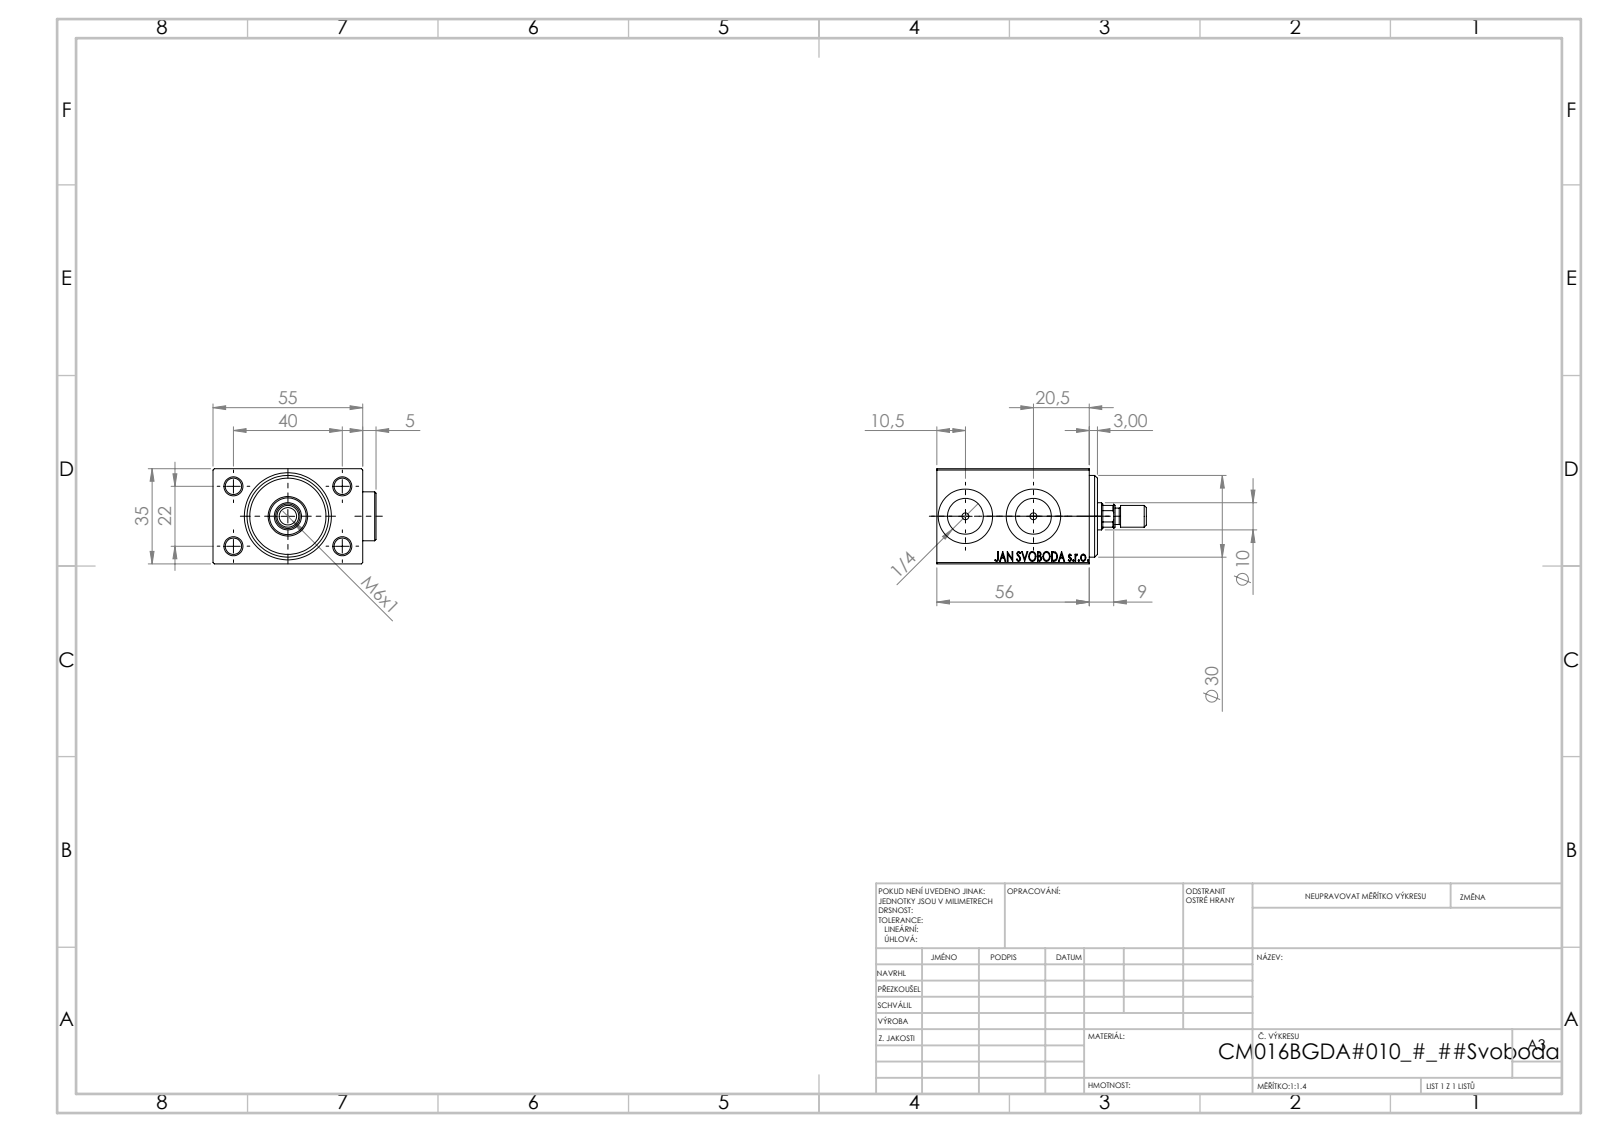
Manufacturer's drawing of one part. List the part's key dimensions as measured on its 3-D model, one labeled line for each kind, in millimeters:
Part name (STEP PRODUCT): Zatka_OIL_PORT; V450CM_B_Body; V450CM_B_VCP; V450CM_MALE_METRIC (+1 more)
STEP written by: SolidWorks 2019 (CONFIG_CONTROL_DESIGN)
Units: millimetres
Bodies: 6 solids, 949 faces (439 planar, 74 cylindrical, 436 other)
Overall size (bounding box): 77 × 59.9 × 35
Volume: 101 781 mm³ · Surface area: 28 309 mm²
Round holes (diameter × count): ⌀6 ×4, ⌀2.5 ×2, ⌀13.16 ×2, ⌀20 ×2, ⌀4.5 ×1, ⌀10 ×1, ⌀13.5 ×1, ⌀14.5 ×1, ⌀16 ×1, ⌀18 ×1, ⌀30 ×1
Round bosses / shafts (diameter × count): ⌀18 ×2, ⌀8 ×1, ⌀6 ×1
Partial cylindrical surfaces — rounded edges, fillets, slot ends (radius × count): R4.5 ×1
Main face-to-face distances: 35, 5, 51, 55, 54.9, 56, 3, 8, 42, 59
Hole centre spacings: 22.83, 22, 40, 45.65, 25
